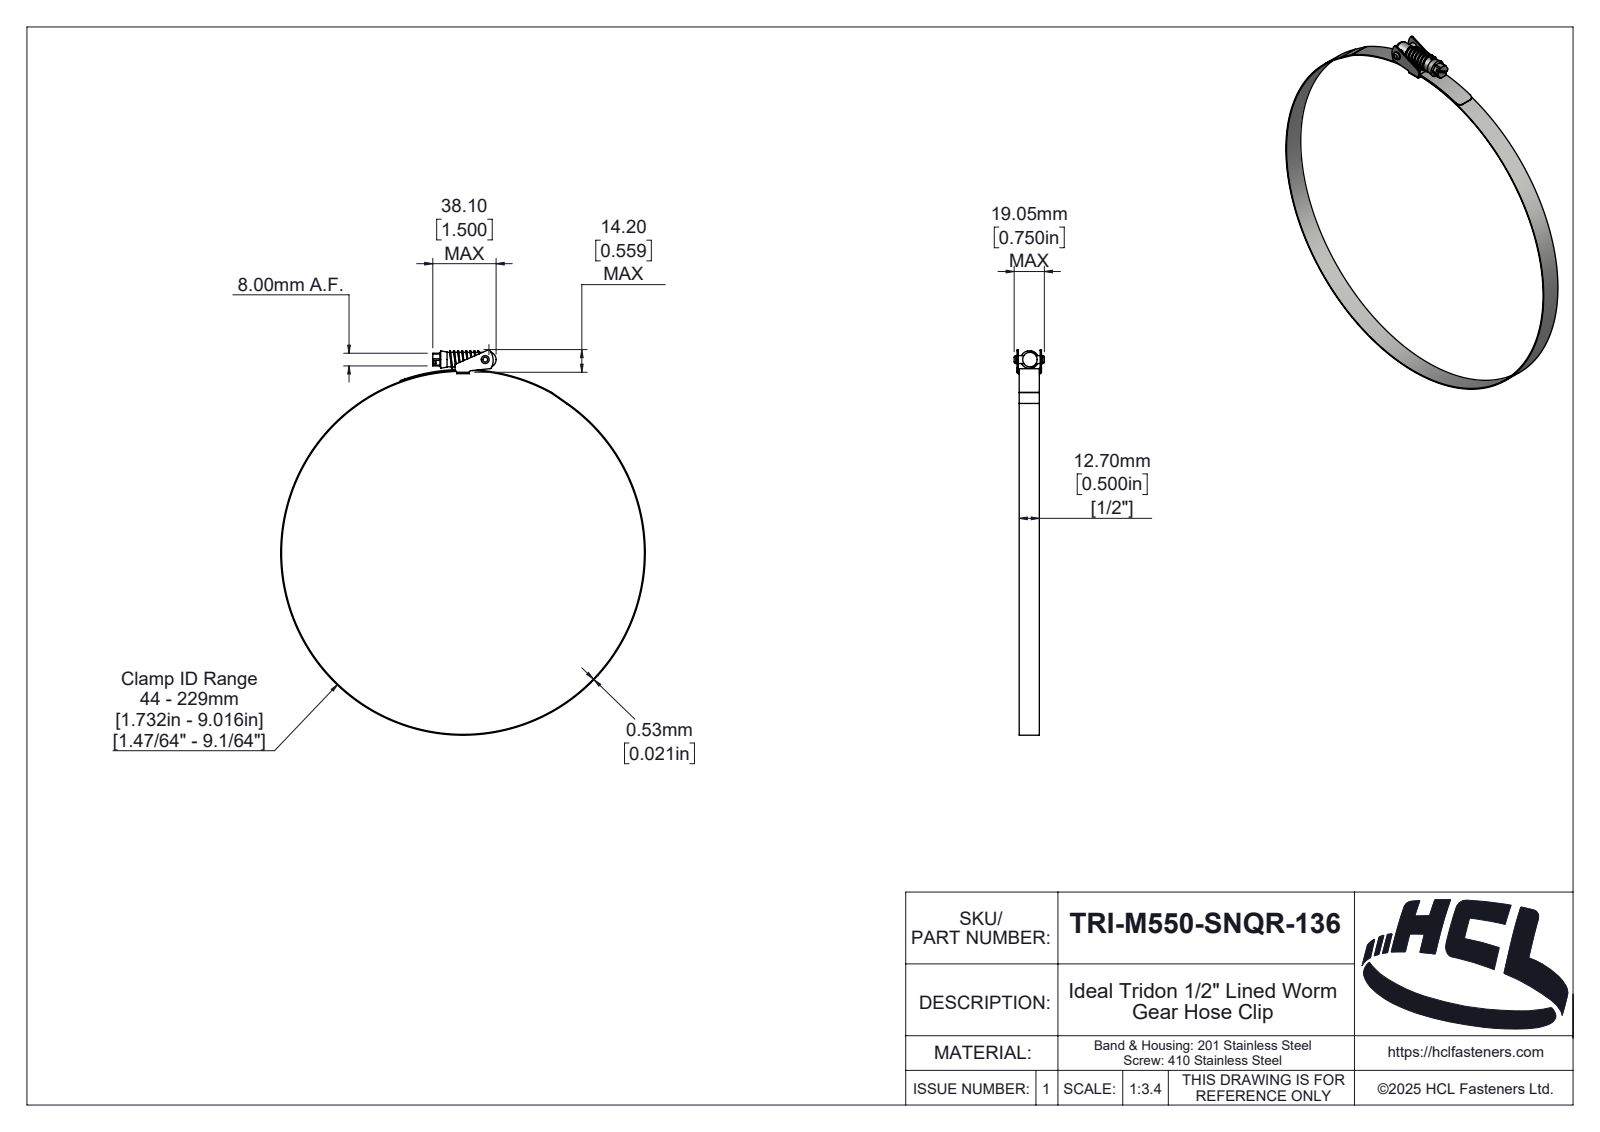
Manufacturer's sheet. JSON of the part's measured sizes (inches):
{"part_name": "TRI-M550-SNQR-136", "step_written_by": "SolidWorks 2025 (AUTOMOTIVE_DESIGN)", "units": "inches", "bodies": {"solids": 5, "faces": 222, "planar": 44, "cylindrical": 112, "other": 66}, "overall_size": [9.568, 9.057, 0.75], "volume_in3": 0.507, "surface_area_in2": 36.79, "round_holes": [[0.197, 1], [9.016, 1]], "round_bosses_or_shafts": [[9.057, 1], [0.358, 1]], "partial_cylinders_radius": [[0.039, 11], [0.004, 2], [0.035, 2], [0.118, 2], [0.018, 1], [0.074, 1], [0.079, 1], [0.093, 1]], "face_to_face_distances": [0.031, 0.5, 0.053, 0.553, 0.575, 0.022, 0.522, 0.606, 0.543, 0.021], "hole_center_spacings": [4.831]}
